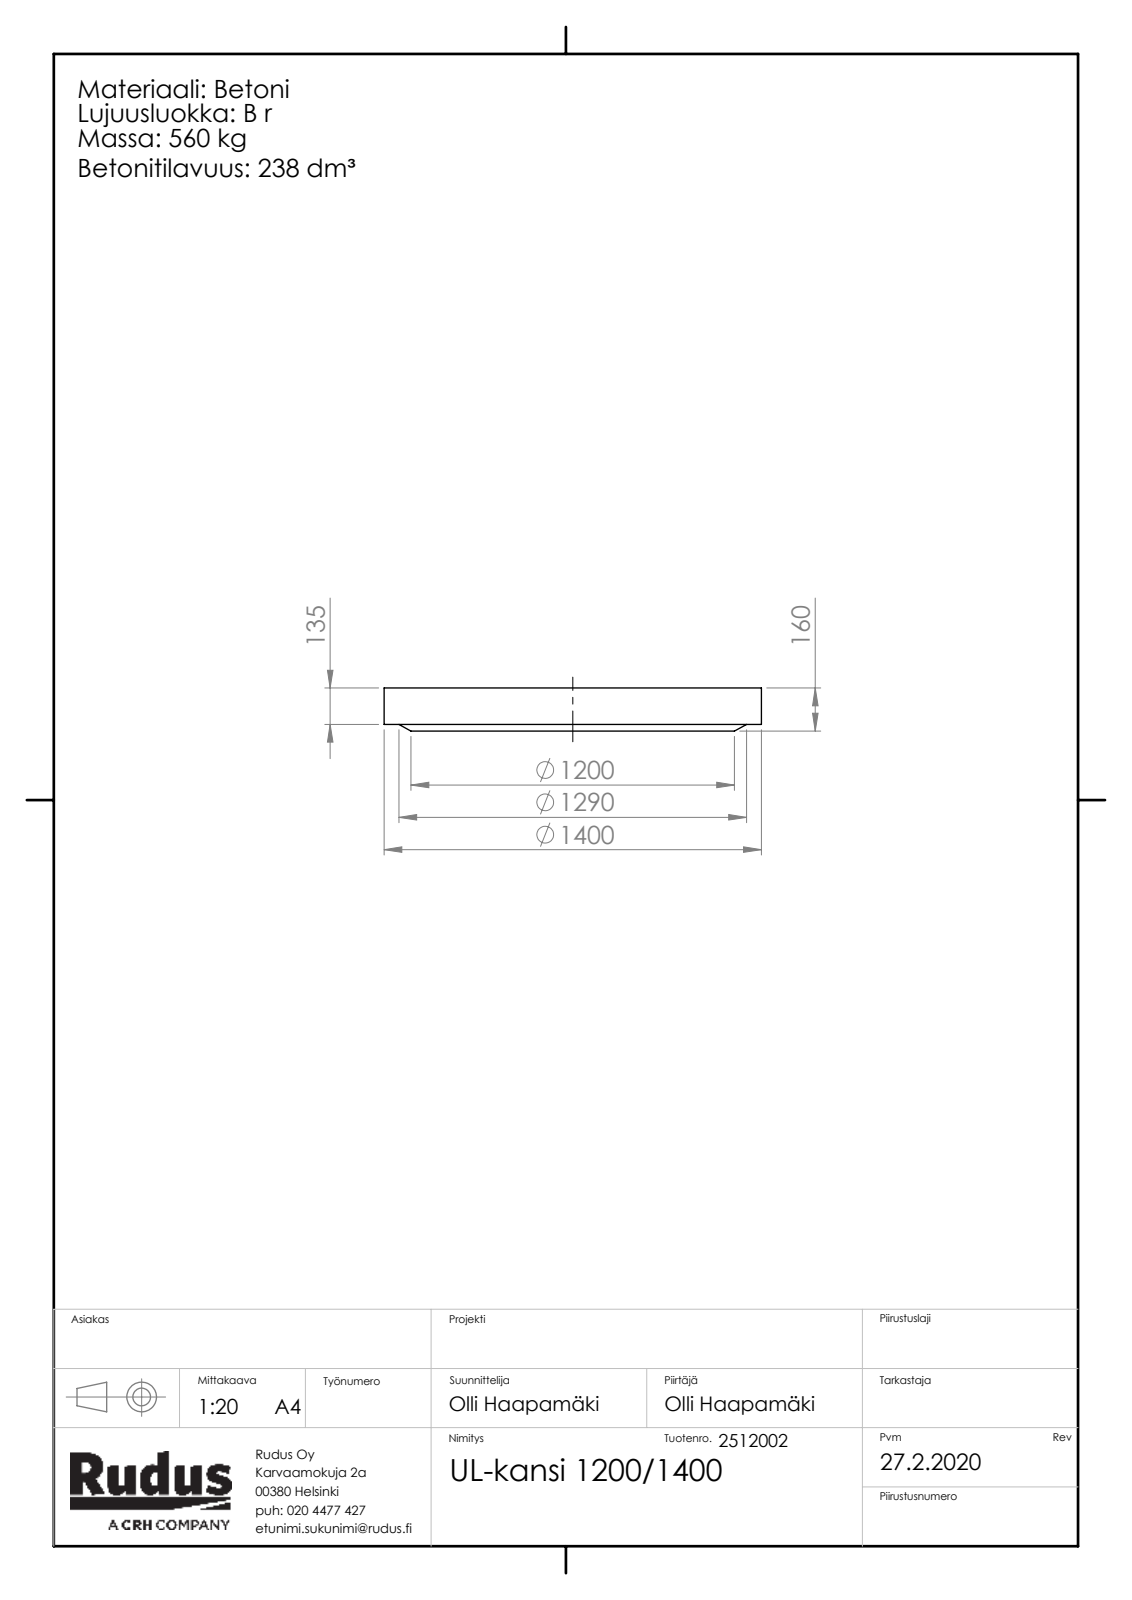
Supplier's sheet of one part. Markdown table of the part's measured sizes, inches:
| quantity | value |
| --- | --- |
| part name | Rudus 2512002 UL-kansi 1200_1400; UL-osa-kansi_umpi |
| STEP written by | SolidWorks 2019 (CONFIG_CONTROL_DESIGN) |
| units | inches |
| bodies | 1 solid, 76 faces (17 planar, 9 cylindrical, 50 other) |
| overall size | 55.118 × 55.118 × 6.299 |
| volume | 14 540 in³ |
| surface area | 5 733 in² |
| round bosses / shafts (diameter × count) | 55.118 × 1 |
| partial cylindrical surfaces (radius × count) | 27.441 × 1 |
| main face-to-face distances | 6.299, 0.984, 5.315, 2.657, 4.429, 3.445, 1.87, 3.642, 0.787, 0.141 |
